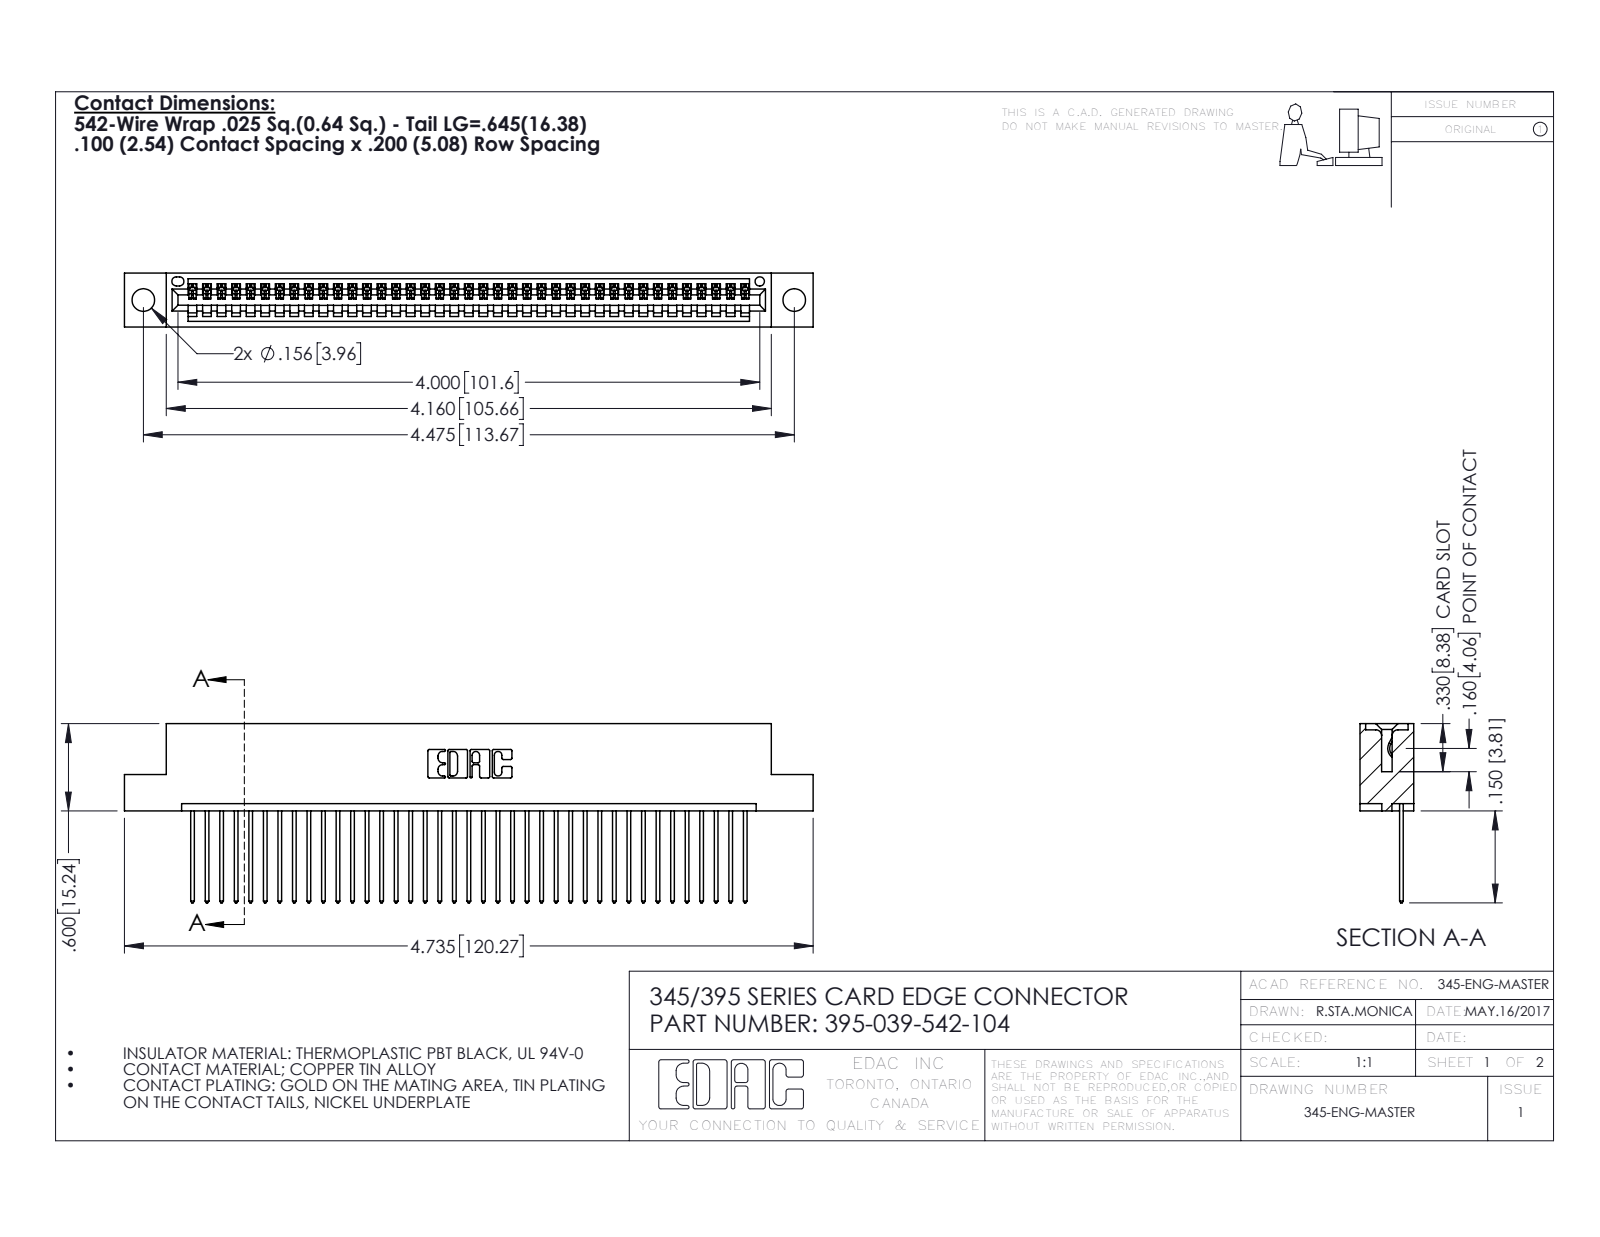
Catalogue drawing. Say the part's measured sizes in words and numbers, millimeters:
The part is named "345 Part_Flush Mounting Lugs - 0.156 Dia-TH; 395-039-542-104; 345-292-001_345-293-142". Its 3-D file was written by "SolidWorks 2016 (CONFIG_CONTROL_DESIGN)". It is 40 solids with 2388 faces: 1640 planar, 748 cylindrical and 0 other. Overall it measures 120.3 by 31.3 by 9.4 millimeters. Its volume is 11 400 cubic millimeters and its surface area 15 460 square millimeters. Round holes: 2 of diameter 4, 1 of diameter 1.6. Partial cylindrical surfaces (rounded edges, fillets, slot ends): 78 of radius 0.2, 78 of radius 0.3, 22 of radius 0.3, 6 of radius 0.2, 6 of radius 0.8, 3 of radius 0.7, 2 of radius 0.8, 2 of radius 1. The main face-to-face distances are 7.6, 1.8, 9.4, 2.5, 6.9, 0.6, 5.1, 5.7, 3.8, 1.8. The hole center spacings are 6.9, 107.7, 113.7.
